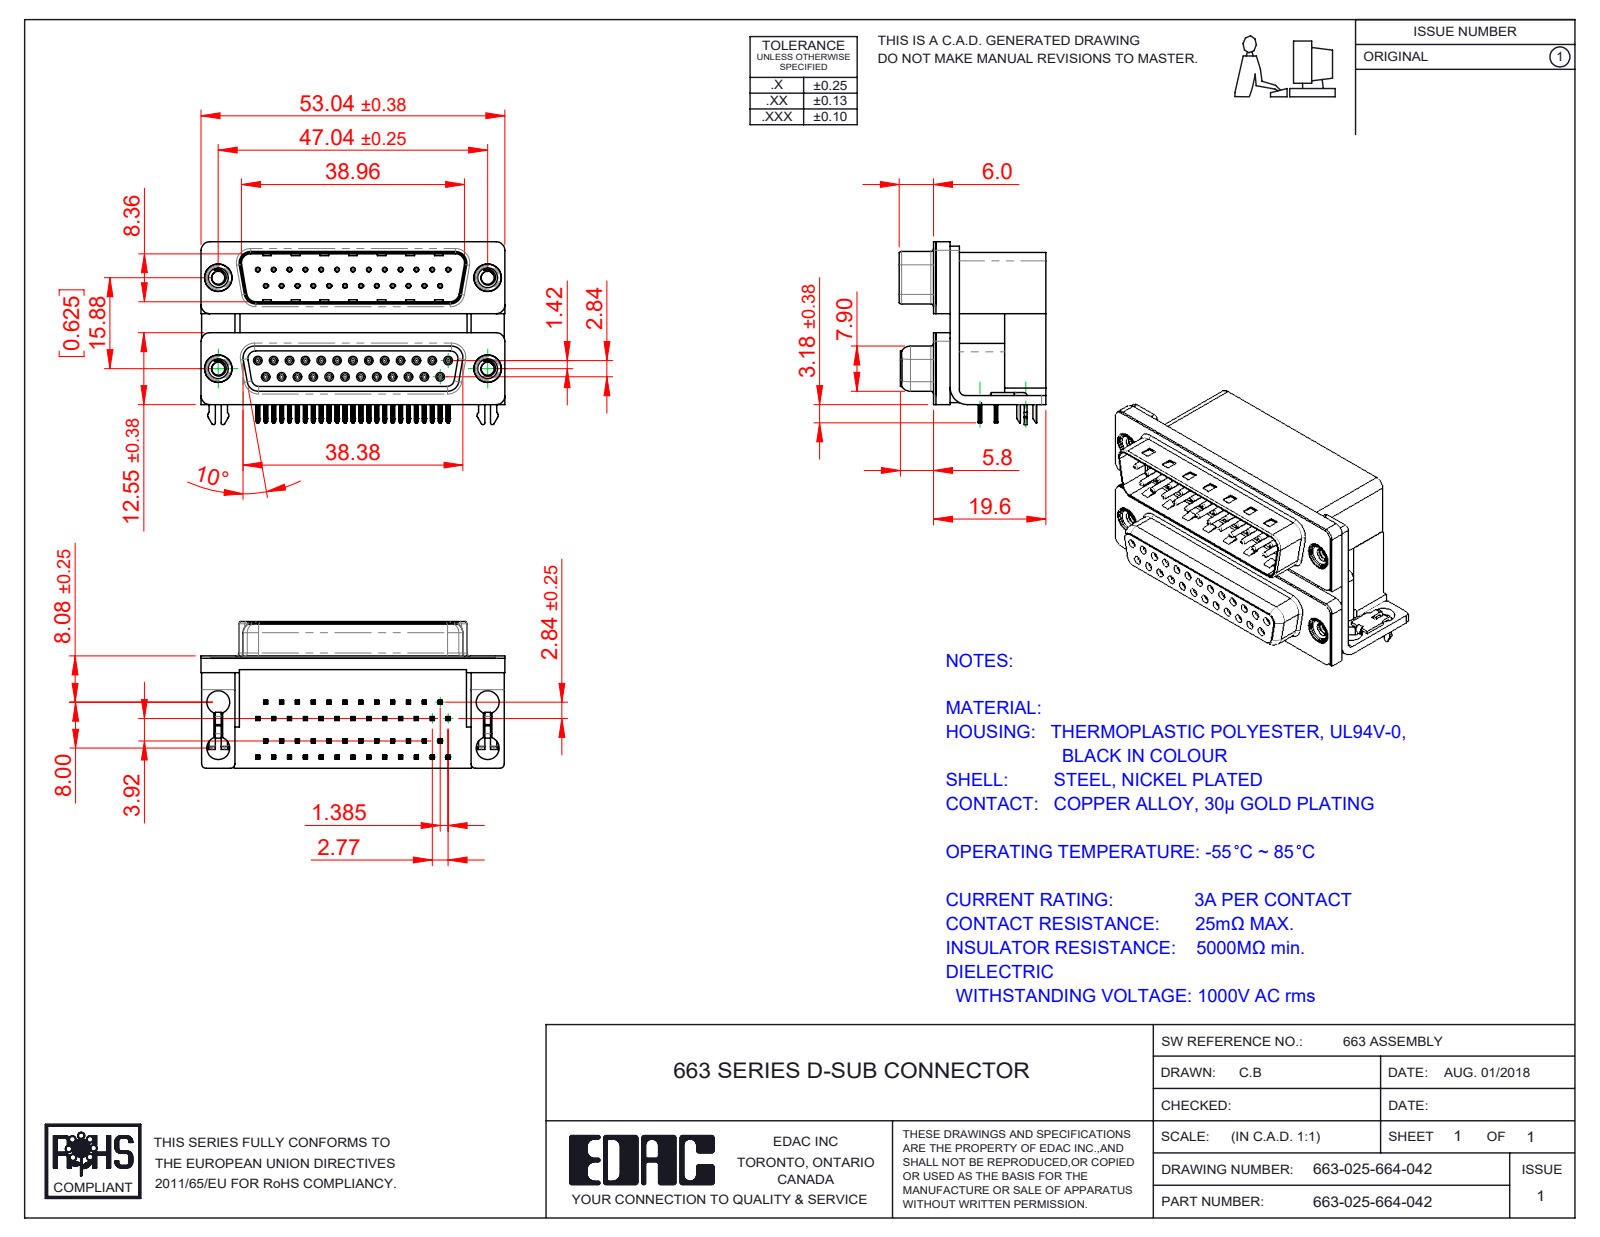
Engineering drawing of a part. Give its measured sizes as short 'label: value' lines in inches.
name: 663 Contact Top Lower; 663 Mounting Bracket_2ProngL; 663 Contact Bottom Lower; 663 Contact Bottom Upper_L (+8 more)
written by: SolidWorks 2020 (CONFIG_CONTROL_DESIGN)
unit: in
bodies: 63 solids, 6311 faces (3335 planar, 1573 cylindrical, 1403 other)
size: 2.088 × 1.257 × 1.008
volume: 1.319 in³; area: 35.94 in²
holes: 50× ⌀0.031, 25× ⌀0.014, 25× ⌀0.035, 8× ⌀0.157, 4× ⌀0.089, 4× ⌀0.138, 4× ⌀0.189, 4× ⌀0.197
bosses: 25× ⌀0.047, 25× ⌀0.03, 4× ⌀0.193, 4× ⌀0.187, 4× ⌀0.154
rounds: 201× R0.004, 106× R0.01, 100× R0.006, 50× R0.005, 50× R0.014, 25× R0.013, 16× R0.02, 13× R0.059
face distances: 0.016, 0.756, 0.283, 0.472, 0.421, 0.657, 0.374, 0.098, 0.611, 1.033
hole spacings: 0.124, 0.109, 0.218, 0.436, 0.327, 0.198, 0.545, 0.294
